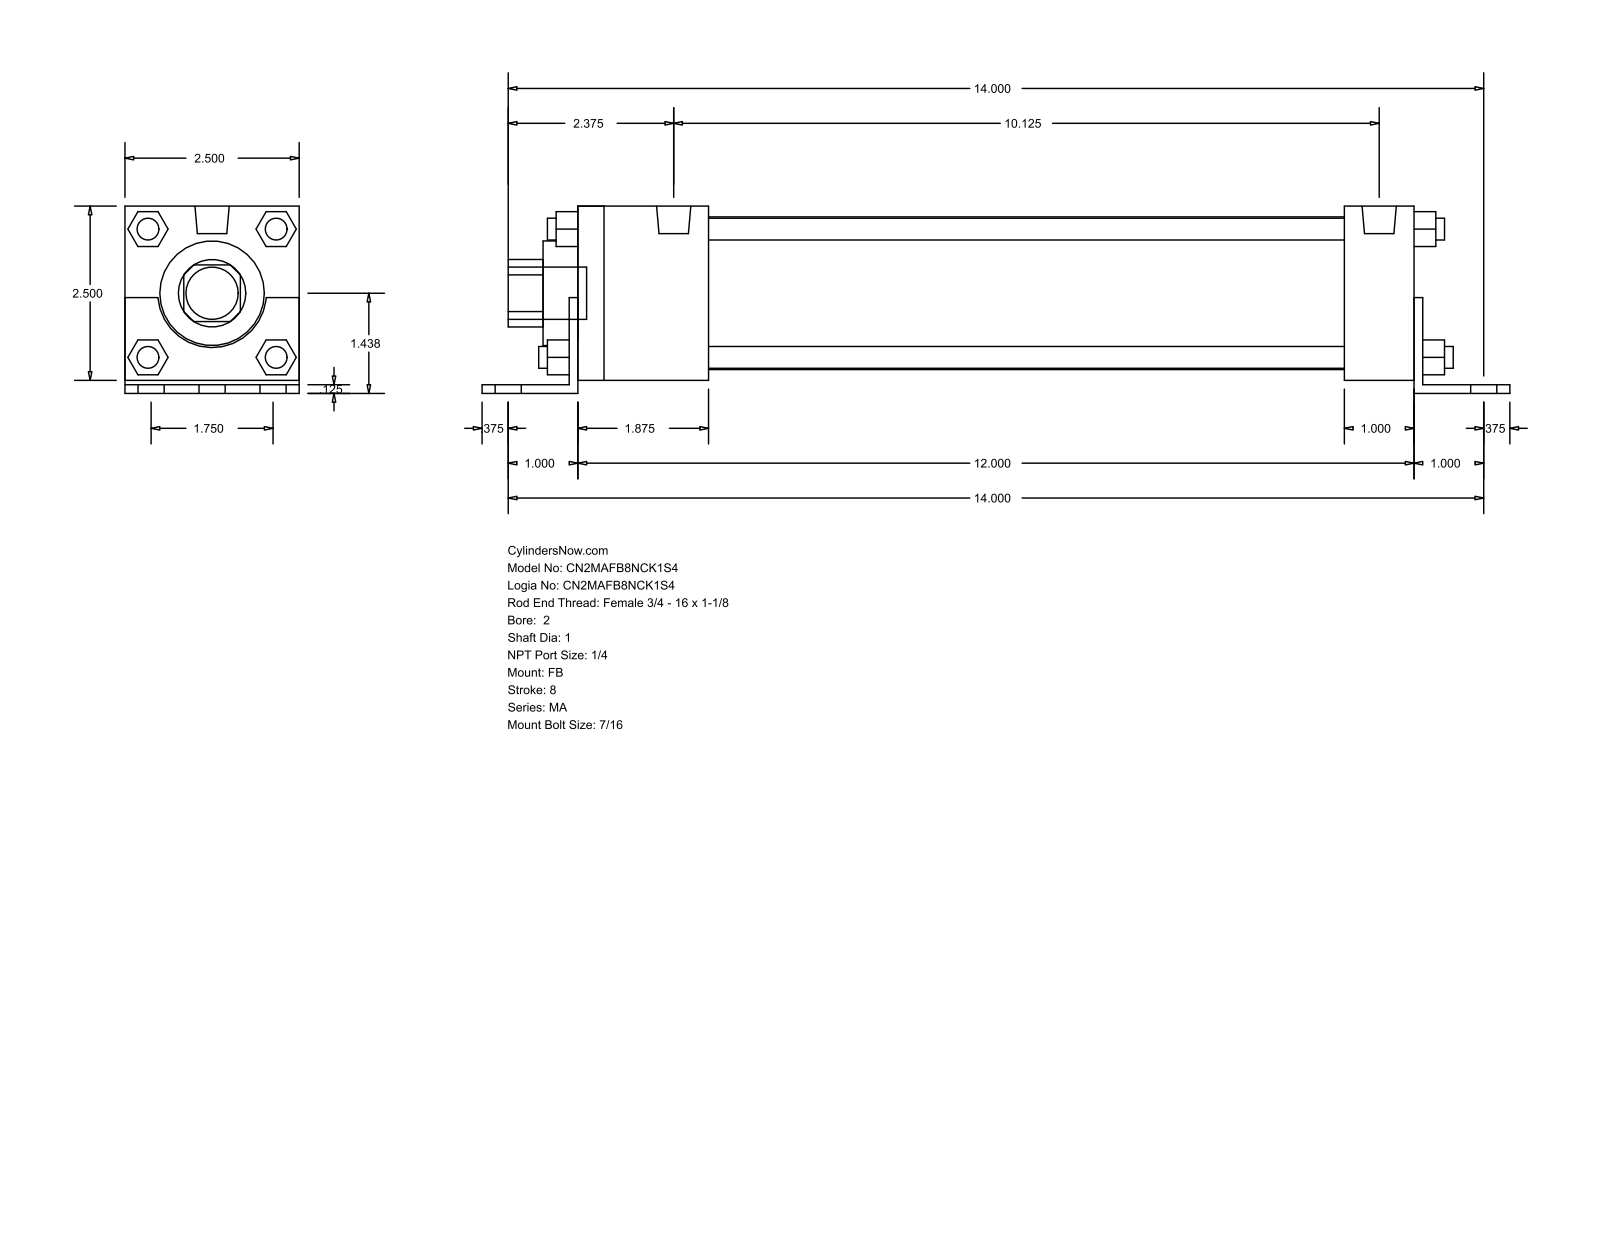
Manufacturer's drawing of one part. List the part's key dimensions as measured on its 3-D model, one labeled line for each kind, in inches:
Part name (STEP PRODUCT): MA_FB__0200_1
STEP written by: GSSL Pune (CONFIG_CONTROL_DESIGN)
Units: inches
Bodies: 0 solids, 140 faces (105 planar, 35 cylindrical, 0 other)
Overall size (bounding box): 14.75 × 2.687 × 2.5
Round holes (diameter × count): ⌀1 ×1, ⌀1.5 ×1, ⌀2.19 ×1
Round bosses / shafts (diameter × count): ⌀0.313 ×8, ⌀0.437 ×6, ⌀0.492 ×2, ⌀0.75 ×1
Partial cylindrical surfaces — rounded edges, fillets, slot ends (radius × count): R0.484 ×1, R0.78 ×1
Main face-to-face distances: 2.5, 0.125, 0.187, 2.687, 0.063, 2.563, 0.5, 0.125, 12, 12.125
